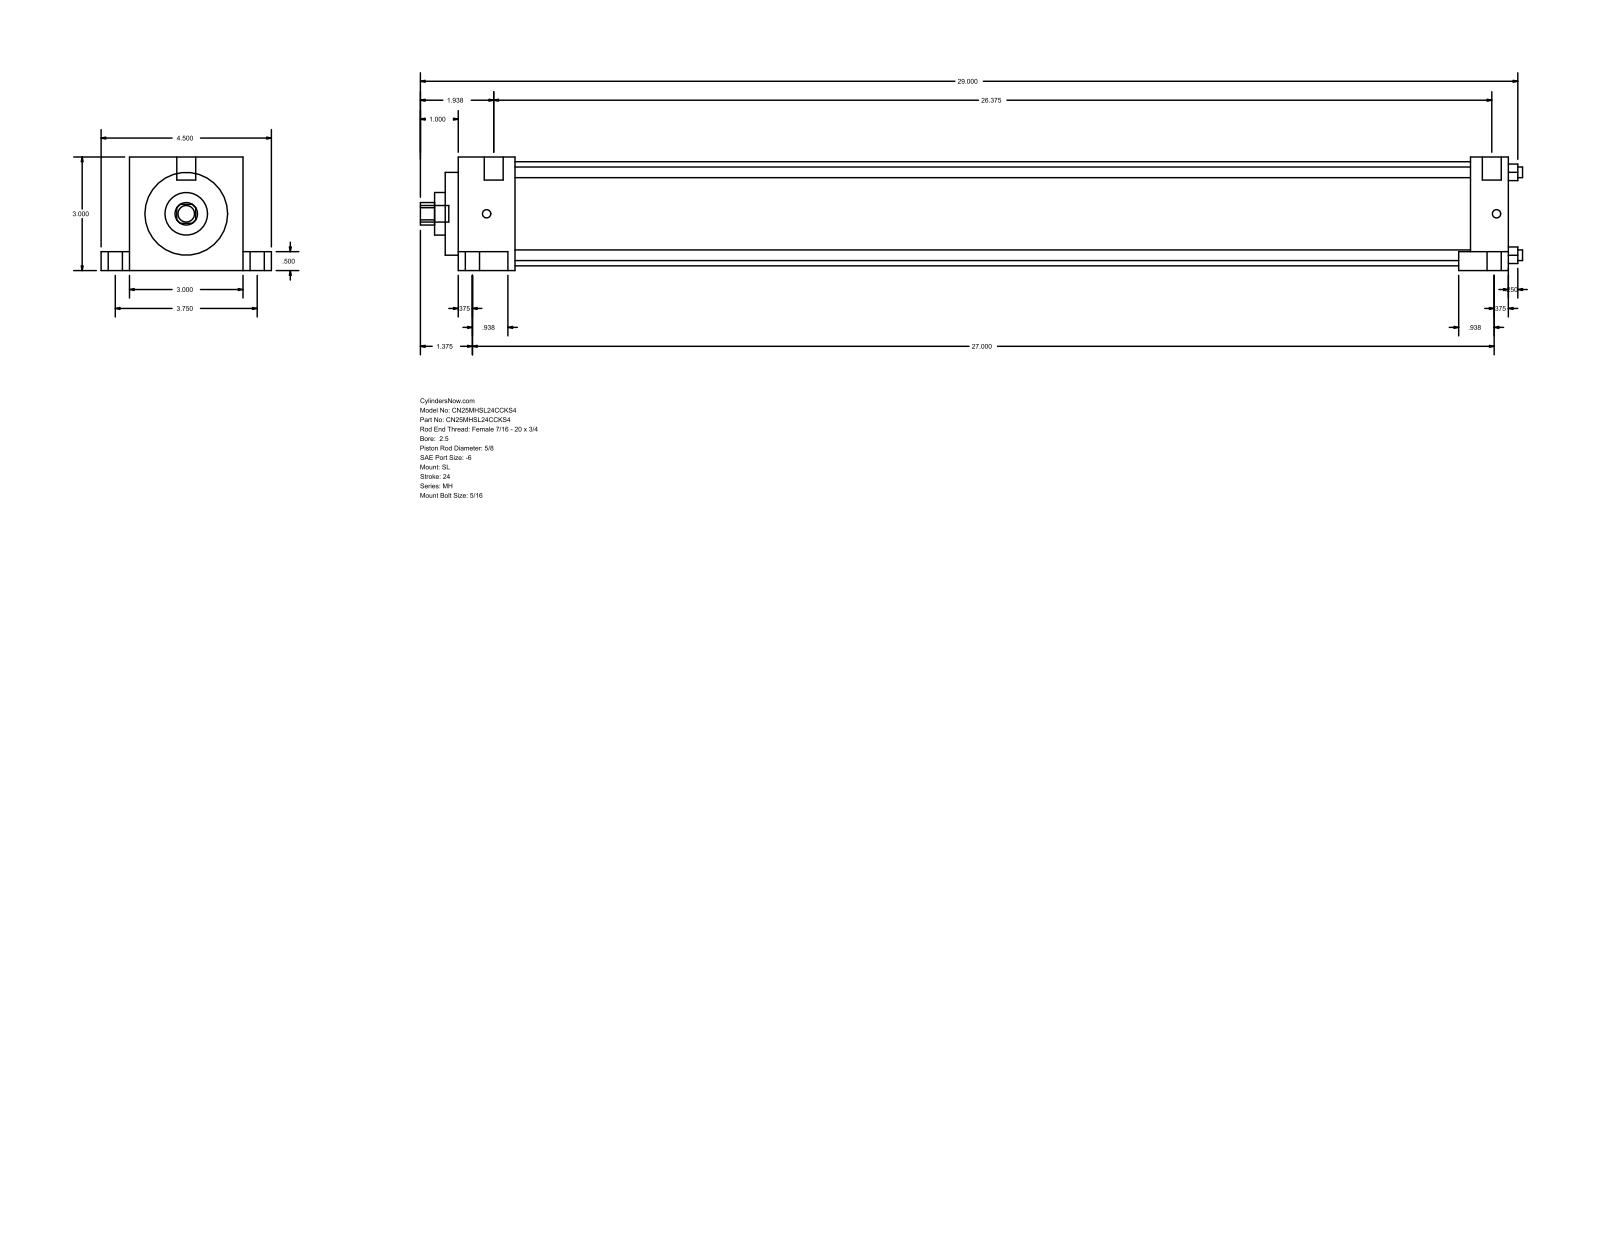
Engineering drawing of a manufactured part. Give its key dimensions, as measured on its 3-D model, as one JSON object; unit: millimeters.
{"part_name": "MH_SL__0250_0.625", "step_written_by": "GSSL Pune (CONFIG_CONTROL_DESIGN)", "units": "millimeters", "bodies": {"solids": 0, "faces": 86, "planar": 61, "cylindrical": 25, "other": 0}, "overall_size": [739.77, 114.3, 76.2], "round_holes": [[7.14, 4], [15.88, 1], [28.57, 1], [55.55, 1], [69.85, 1]], "round_bosses_or_shafts": [[15.88, 2], [9.53, 2], [5.56, 2], [12.7, 1], [11.11, 1]], "partial_cylinders_radius": [[7.54, 1]], "face_to_face_distances": [76.2, 25.4, 688.18, 713.58, 12.7, 63.5, 19.05, 95.25, 720.72, 31.75], "hole_center_spacings": [39.33, 55.62, 78.66]}
